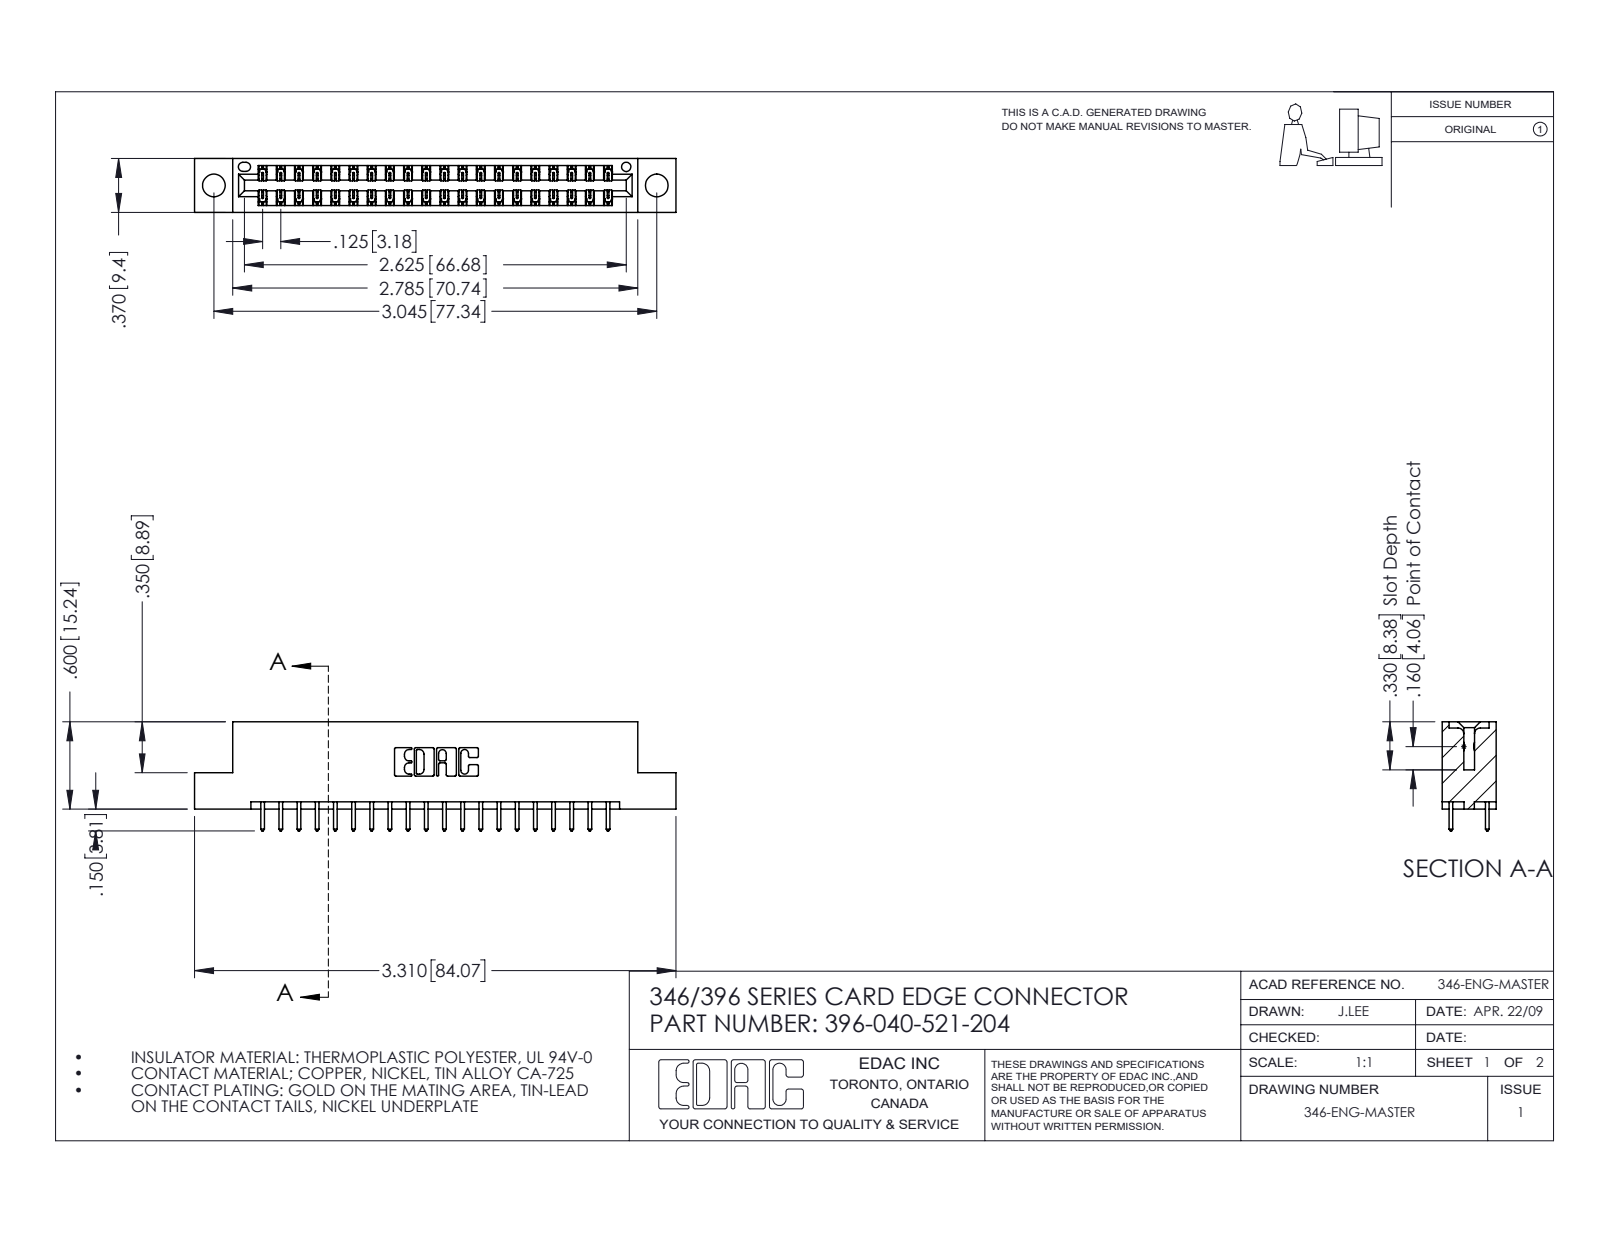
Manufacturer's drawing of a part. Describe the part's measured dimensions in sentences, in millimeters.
The part is named "345-292-001_345-293-121; 346 Part_Flush Mounting Lugs - 0.156 Dia-TH; 396-040-521-204". Its 3-D file was written by "SolidWorks 2016 (CONFIG_CONTROL_DESIGN)". It is 41 solids with 2202 faces: 1476 planar, 726 cylindrical and 0 other. Overall it measures 84.1 by 19.1 by 9.4 millimeters. Its volume is 7 930 cubic millimeters and its surface area 10 250 square millimeters. Round holes: 2 of diameter 4, 1 of diameter 1.6. Partial cylindrical surfaces (rounded edges, fillets, slot ends): 60 of radius 0.2, 40 of radius 0.3, 22 of radius 0.3, 6 of radius 0.2, 6 of radius 0.8, 3 of radius 0.7, 2 of radius 0.4, 2 of radius 0.6. The main face-to-face distances are 1.2, 8.2, 6.4, 9.4, 1.8, 7.6, 0.6, 7, 3.8, 5.6. The hole center spacings are 6.2, 72.1, 77.3.
